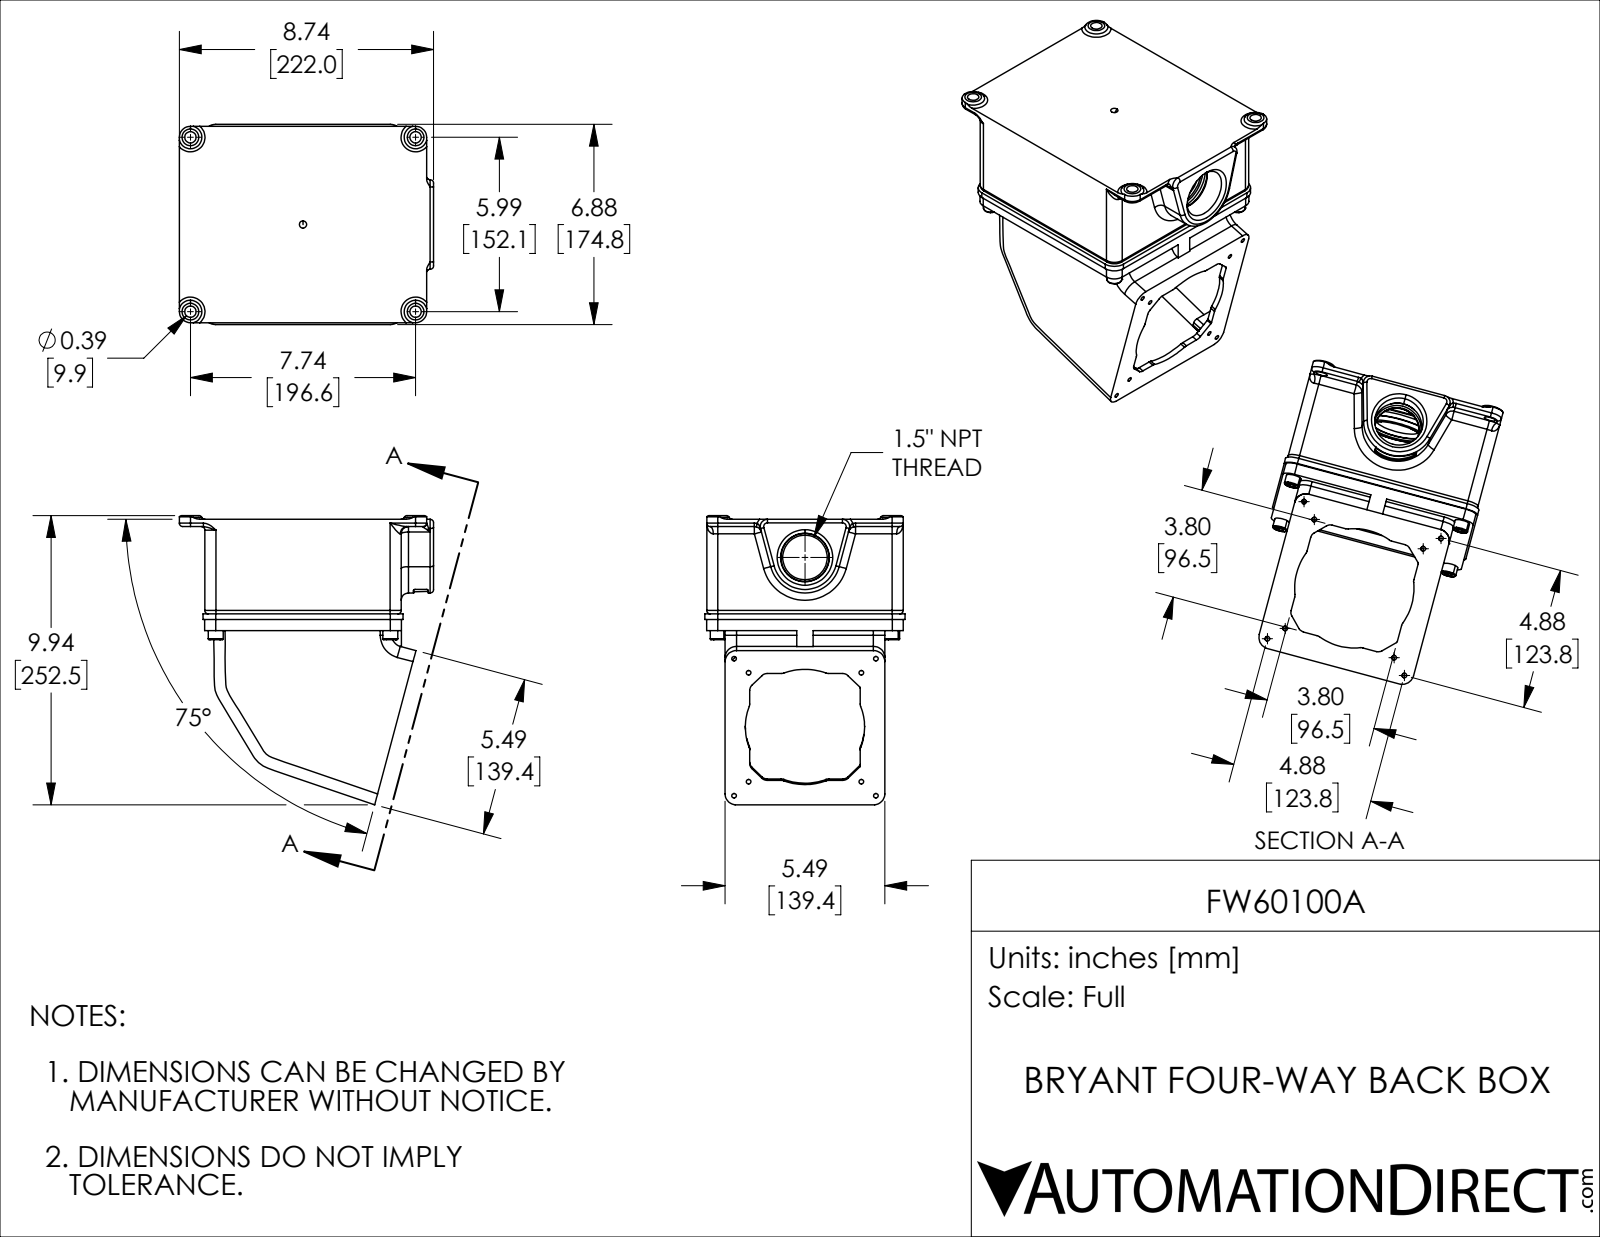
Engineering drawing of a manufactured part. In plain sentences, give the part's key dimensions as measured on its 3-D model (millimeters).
The part is named "FW60100A". Its 3-D file was written by "SolidWorks 2021 (CONFIG_CONTROL_DESIGN)". It is 8 solids with 696 faces: 213 planar, 252 cylindrical and 231 other. Overall it measures 252.45 by 222 by 174.75 millimeters. Its volume is 1 163 000 cubic millimeters and its surface area 422 950 square millimeters. Round holes: 8 of diameter 4.04, 4 of diameter 7.94, 4 of diameter 8.61, 4 of diameter 9.91, 4 of diameter 12.7, 1 of diameter 4.06, 1 of diameter 38.86, 1 of diameter 42.42, 1 of diameter 44.45, 1 of diameter 49.78. Round bosses or shafts: 4 of diameter 13, 4 of diameter 8, 1 of diameter 61.98. Partial cylindrical surfaces (rounded edges, fillets, slot ends): 90 of radius 3.05, 21 of radius 1.52, 13 of radius 6.35, 12 of radius 9.65, 5 of radius 10, 4 of radius 11.18, 2 of radius 4.83, 2 of radius 7.87. The main face-to-face distances are 4.71, 4.83, 134.73, 6.35, 145.91, 11.18, 81.03, 87.38, 150.62, 15.89. The hole center spacings are 152.27, 152.14, 17.96, 22.1, 22.23, 107.58, 107.76, 111.84.
